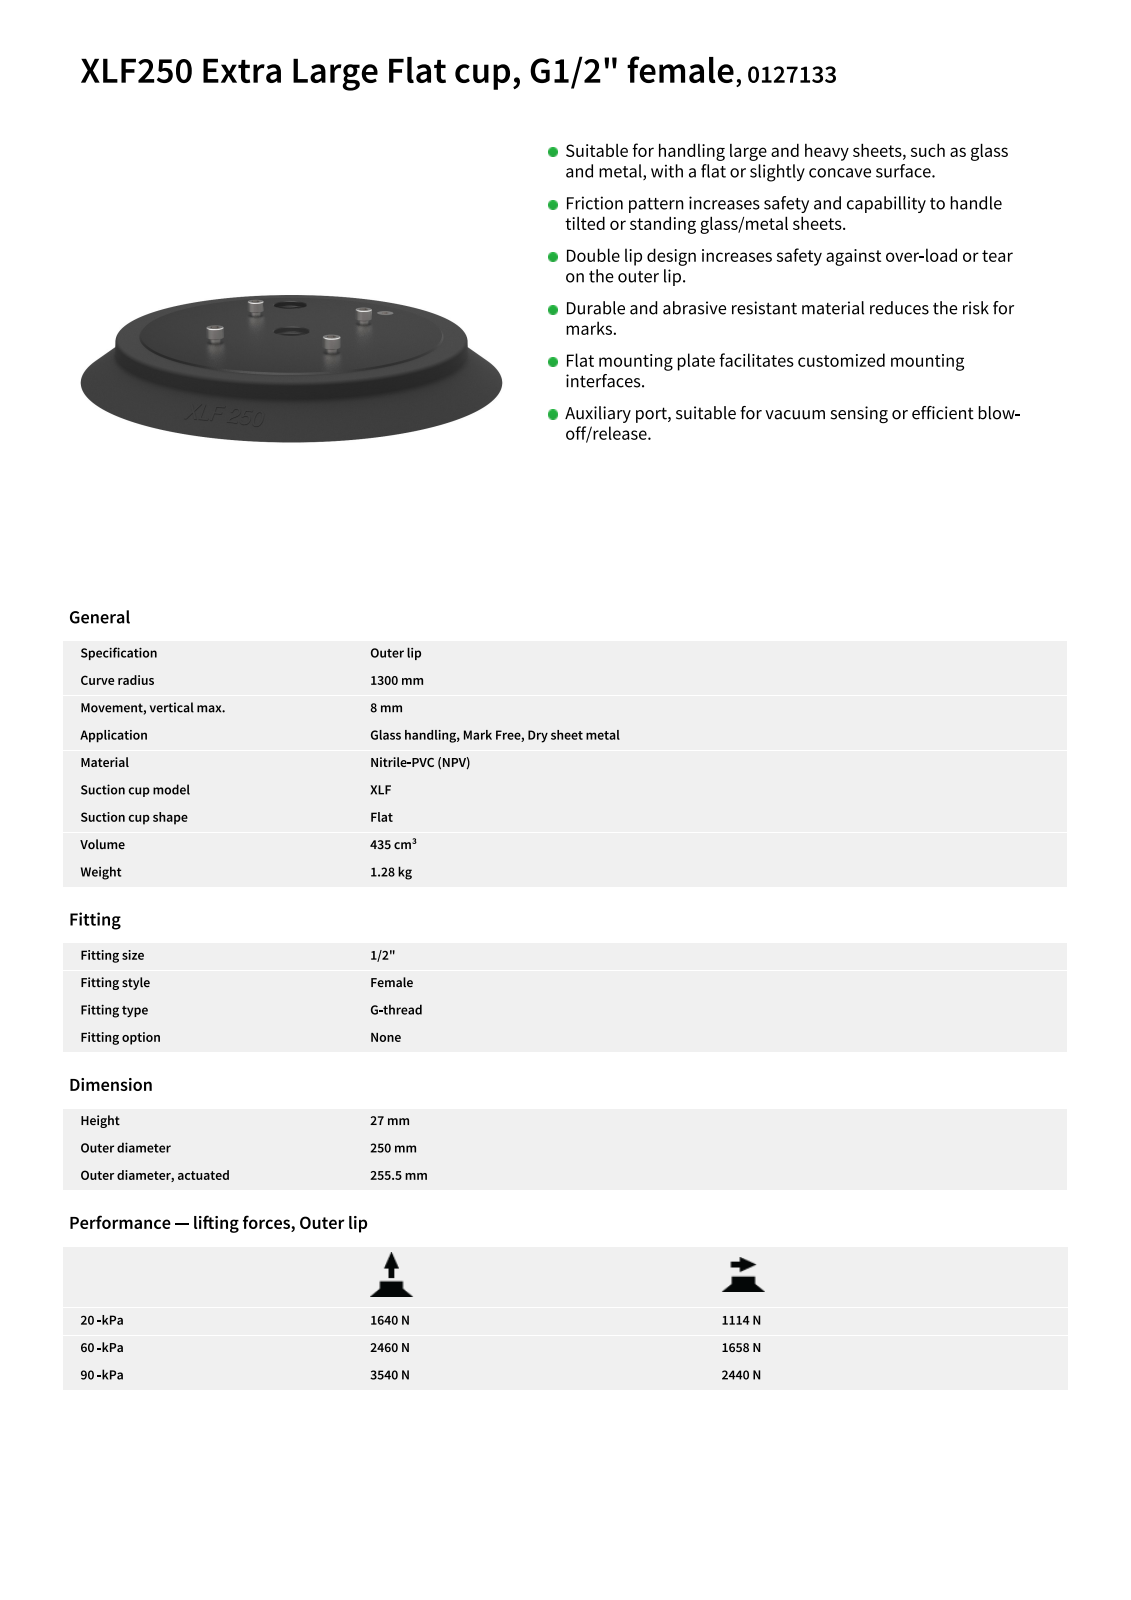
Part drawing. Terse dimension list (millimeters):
name: 0126659; 0126660; SE-0400721; 0106990 (+4 more)
written by: Unknown (AUTOMOTIVE_DESIGN)
unit: mm
bodies: 10 solids, 818 faces (199 planar, 93 cylindrical, 526 other)
size: 250 × 250 × 35
volume: 596 098 mm³; area: 219 009 mm²
holes: 4× ⌀4.92, 2× ⌀19, 2× ⌀21.3, 1× ⌀4, 1× ⌀8.7, 1× ⌀10, 1× ⌀15, 1× ⌀32, 1× ⌀35, 1× ⌀180, 1× ⌀200
bosses: 4× ⌀10, 4× ⌀6, 4× ⌀4.91, 2× ⌀21.7, 2× ⌀21, 2× ⌀20.96, 2× ⌀18.8, 1× ⌀10.3
rounds: 40× R0.5
face distances: 3, 12, 15, 5, 7, 10, 6, 13, 18, 17
hole spacings: 49.5, 70, 98.99, 27.89, 32.7, 64.07, 64.41, 68.62
